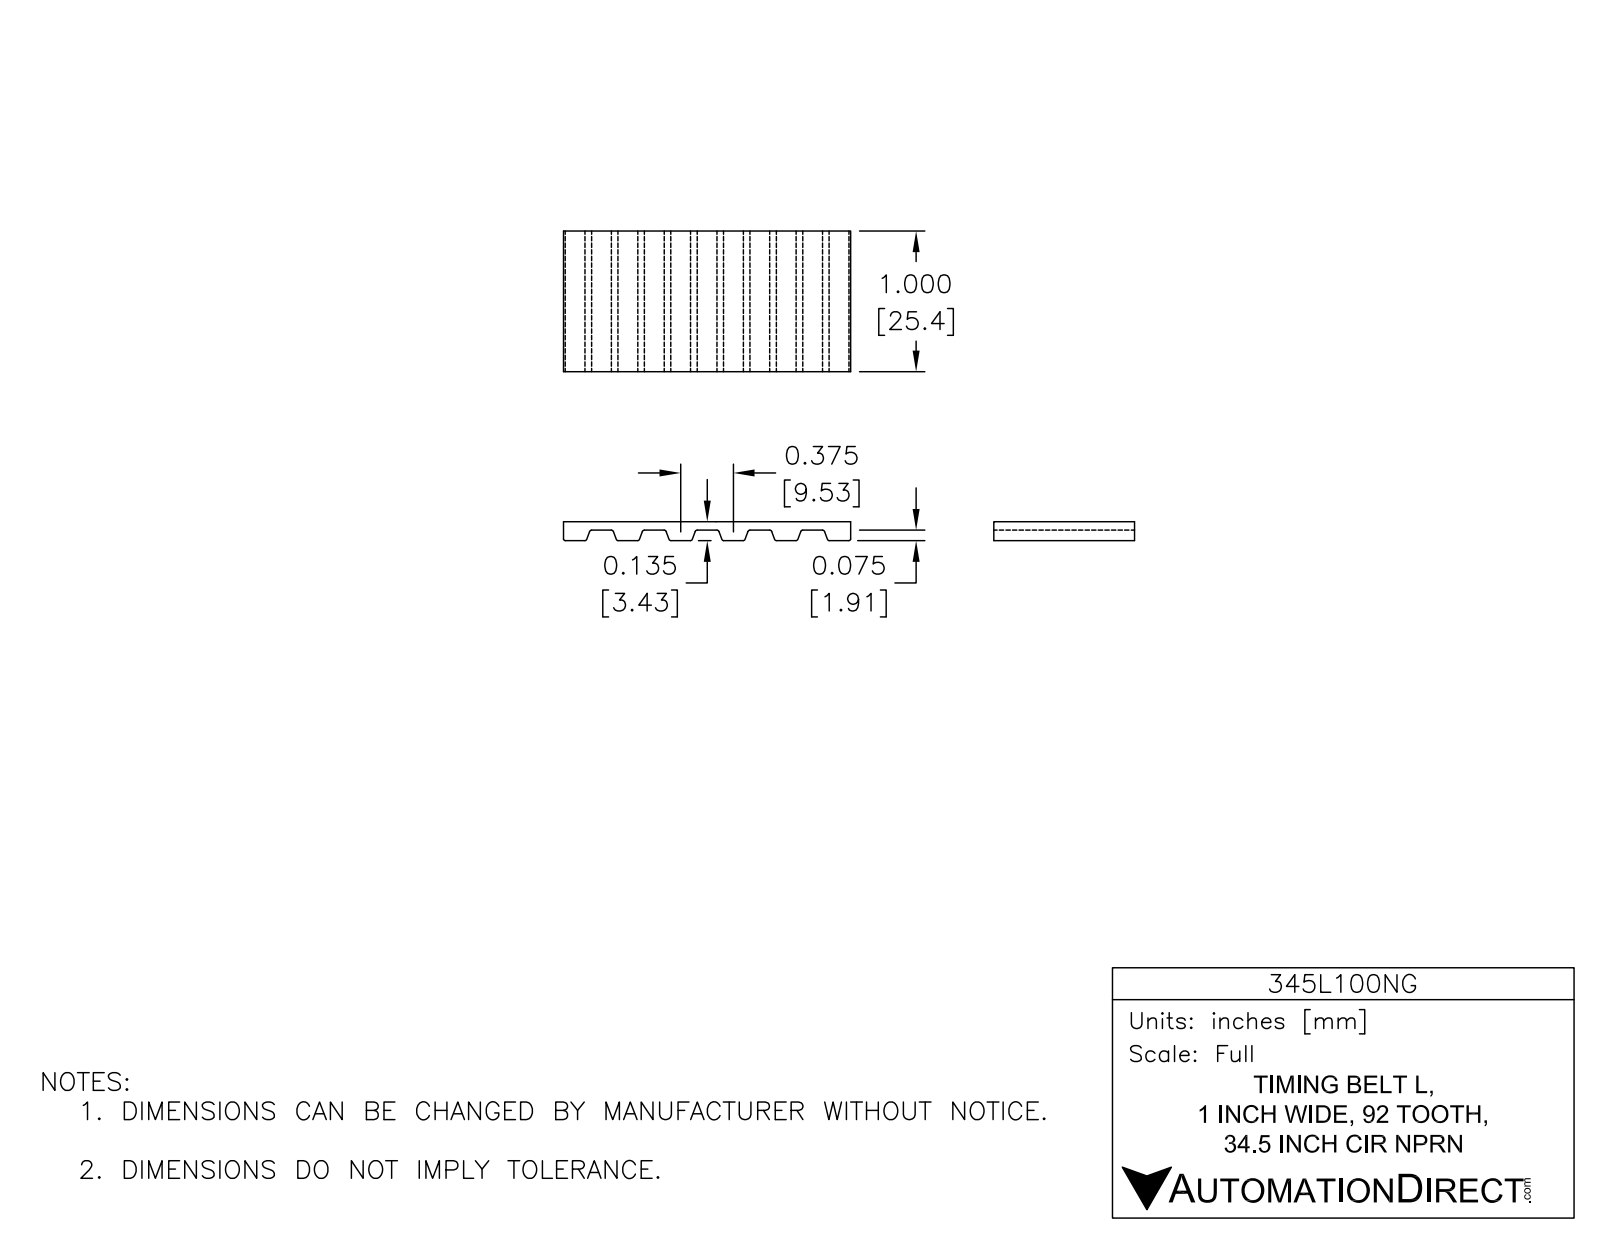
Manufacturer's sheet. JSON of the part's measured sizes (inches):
{"part_name": "345L100NG", "step_written_by": "SolidWorks 2014 (AUTOMOTIVE_DESIGN)", "units": "inches", "bodies": {"solids": 1, "faces": 751, "planar": 345, "cylindrical": 406, "other": 0}, "overall_size": [15.538, 3, 1], "volume_in3": 3.124, "surface_area_in2": 83.08, "partial_cylinders_radius": [[0.02, 364], [1.435, 2], [1.5, 2]], "face_to_face_distances": [0.065, 2.935, 3, 2.87, 0.14, 2.86, 0.075, 2.795, 1, 2.72]}
